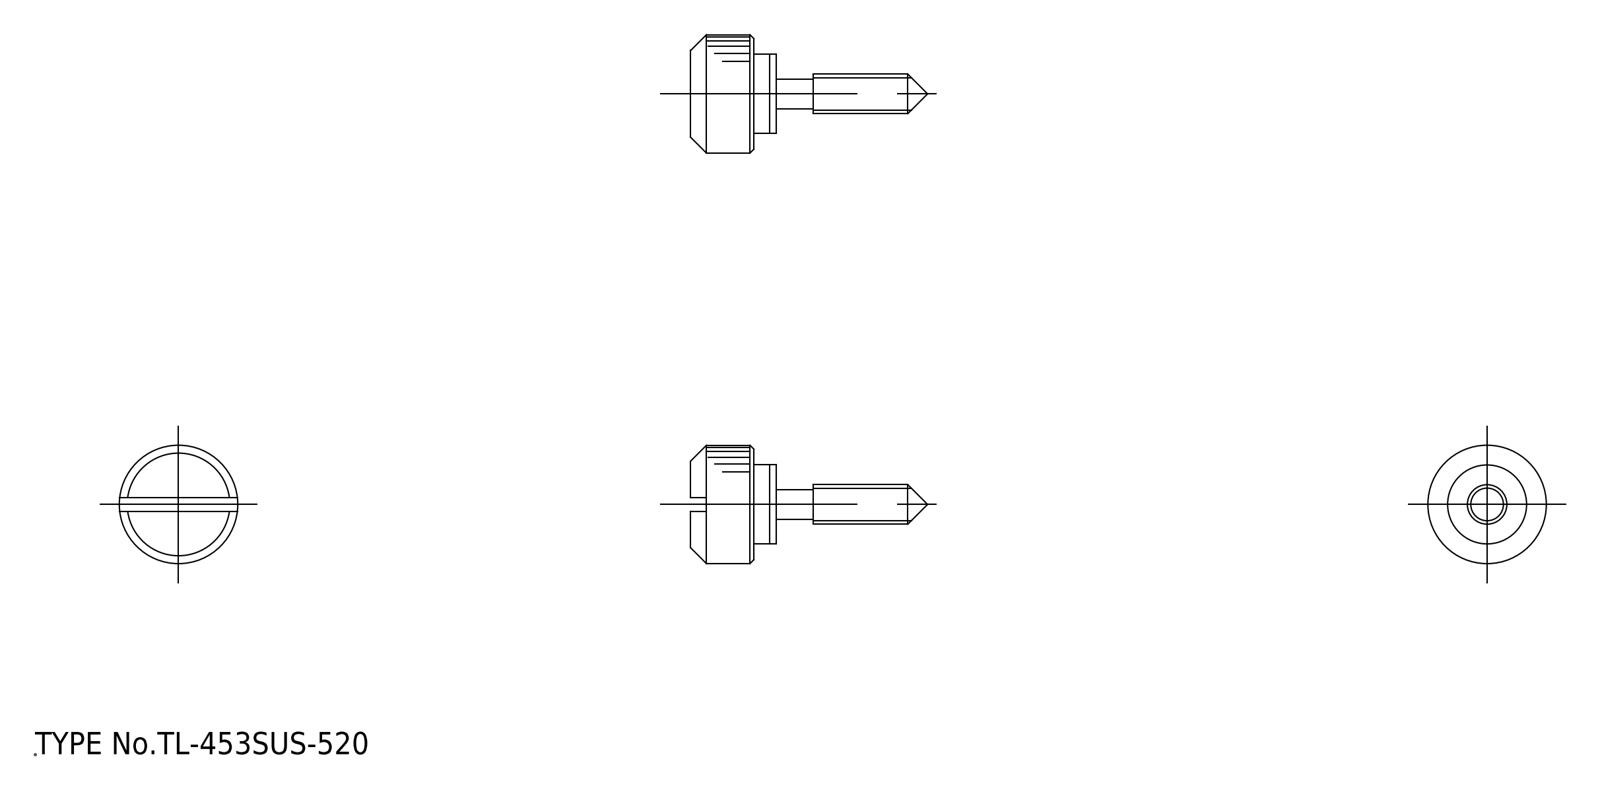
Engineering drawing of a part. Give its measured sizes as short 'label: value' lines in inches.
name: washer; knob
written by: spGate 19.8.4 (****-****-****-****) (AUTOMOTIVE_DESIGN)
unit: in
bodies: 2 solids, 42 faces (18 planar, 18 cylindrical, 6 other)
size: 1.181 × 0.591 × 0.591
volume: 0.11 in³; area: 1.872 in²
bosses: 1× ⌀0.591, 1× ⌀0.394, 1× ⌀0.197, 1× ⌀0.15
rounds: 4× R0.031, 1× R0.077
face distances: 0.079, 0.315, 0.394, 0.425, 0.11, 0.031, 0.236, 0.346, 0.071, 0.61
